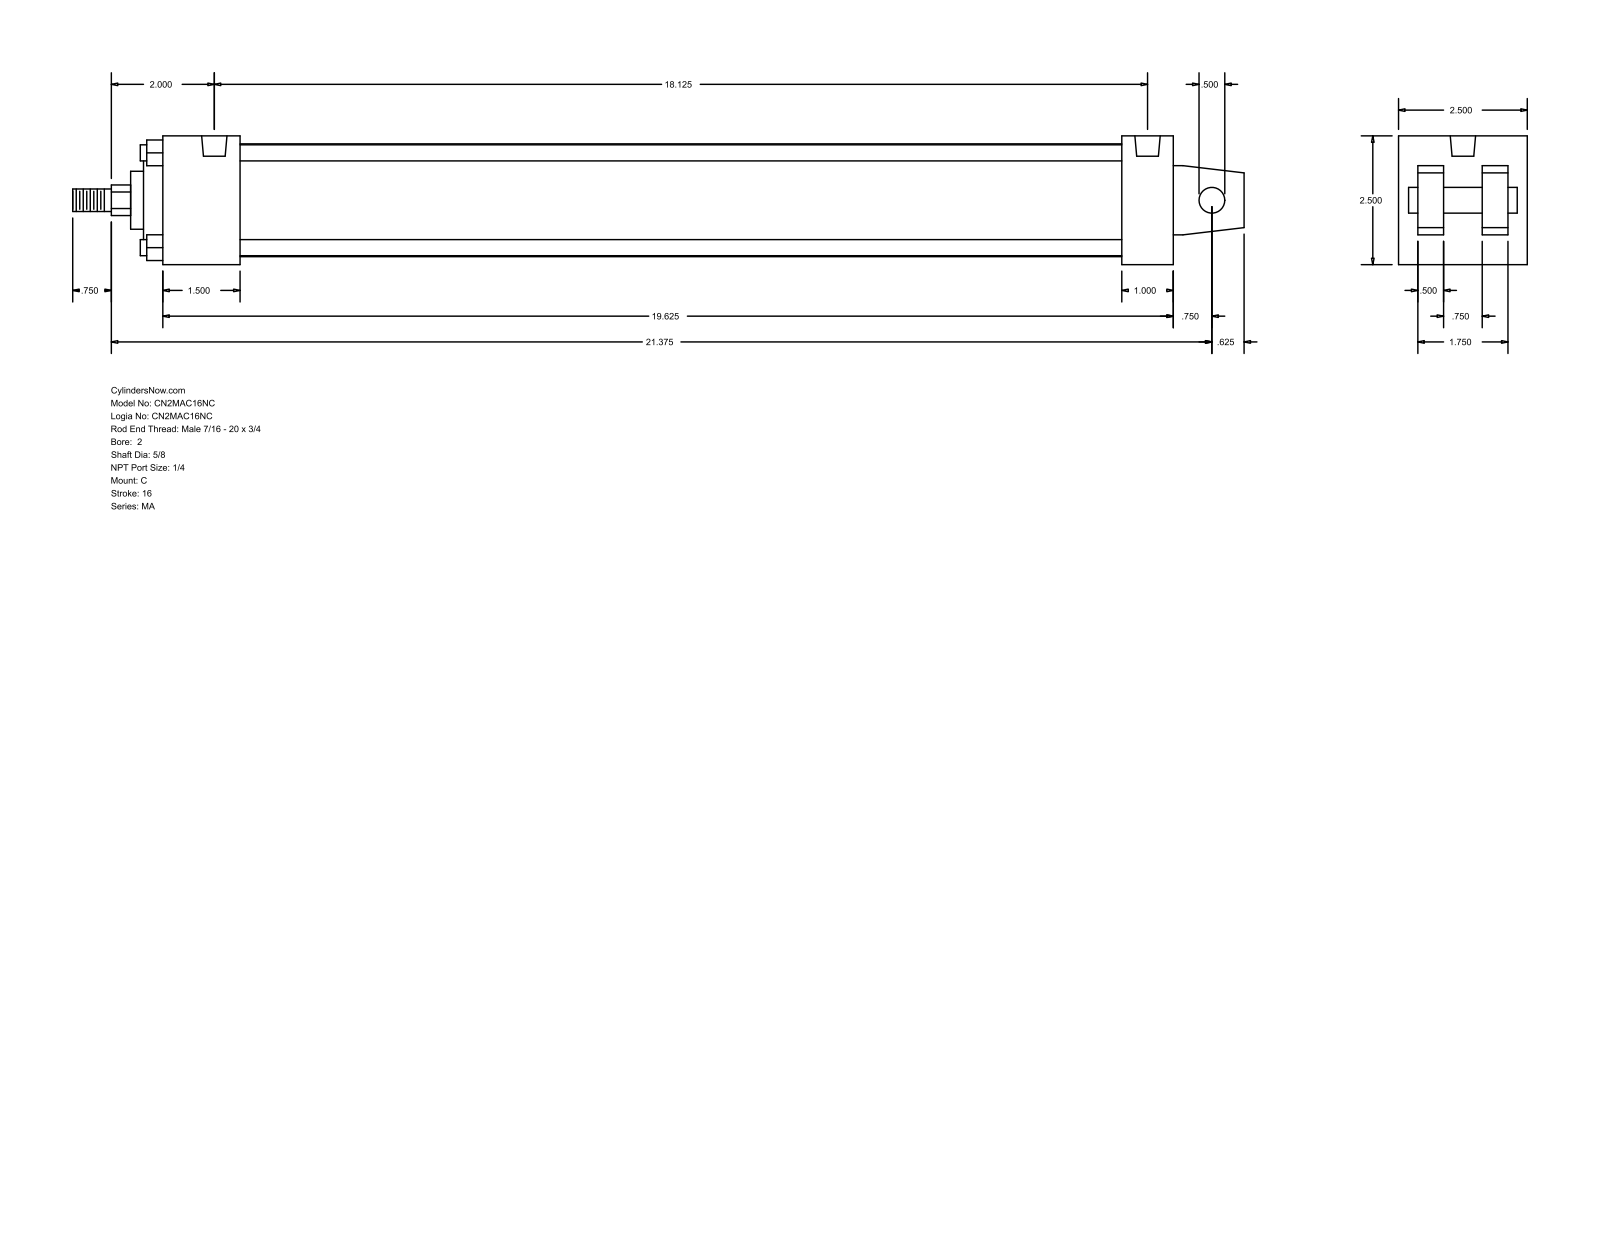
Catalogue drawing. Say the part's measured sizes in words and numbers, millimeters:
The part is named "MA_C__0200_0.625". Its 3-D file was written by "GSSL Pune (CONFIG_CONTROL_DESIGN)". It is 0 solids with 105 faces: 77 planar, 28 cylindrical and 0 other. Overall it measures 577.85 by 63.5 by 63.5 millimeters. Round holes: 4 of diameter 7.94, 2 of diameter 12.49. Round bosses or shafts: 4 of diameter 7.94, 1 of diameter 55.63, 1 of diameter 50.8, 1 of diameter 28.57, 1 of diameter 15.88, 1 of diameter 12.7, 1 of diameter 11.11. Partial cylindrical surfaces (rounded edges, fillets, slot ends): 1 of radius 7.54. The main face-to-face distances are 63.5, 9.52, 12.7, 22.22, 41.28, 53.98, 31.76, 25.4, 38.1, 498.48. The hole center spacings are 460.38.
